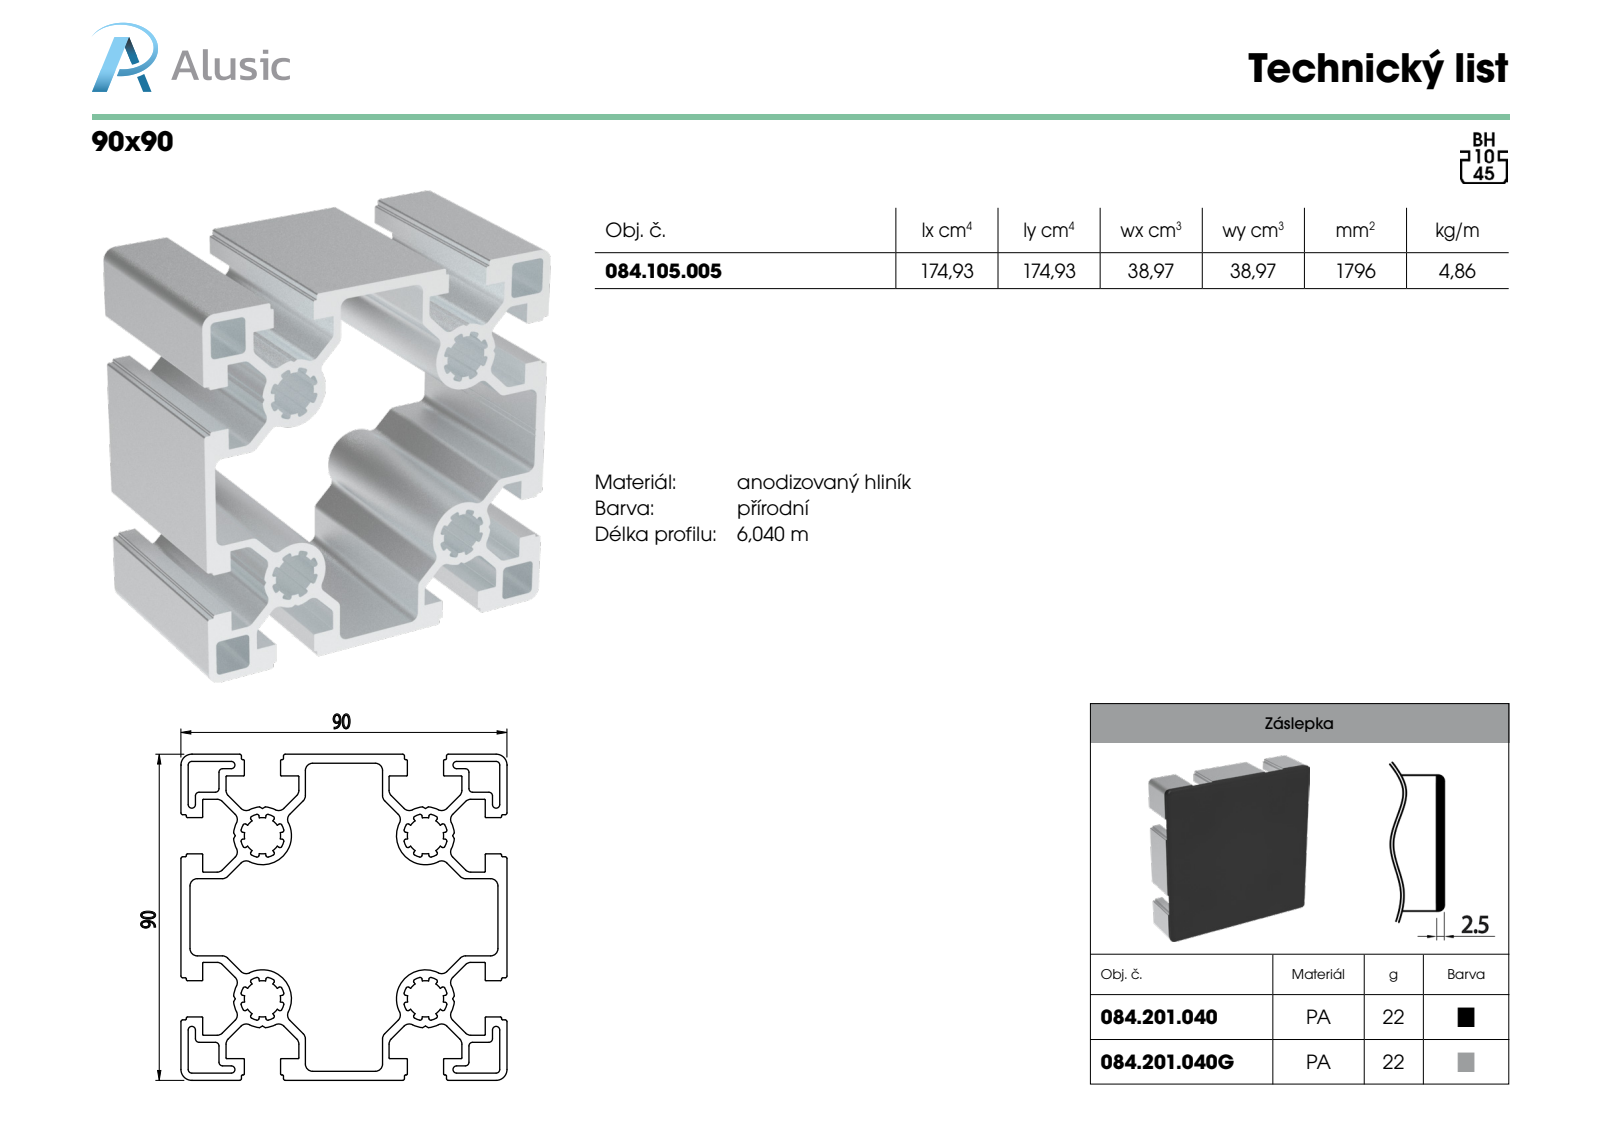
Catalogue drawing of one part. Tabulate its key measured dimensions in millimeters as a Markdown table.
| quantity | value |
| --- | --- |
| part name | 084.201.040 |
| STEP written by | SolidWorks 2011 (CONFIG_CONTROL_DESIGN) |
| units | millimeters |
| bodies | 1 solid, 58 faces (14 planar, 24 cylindrical, 20 other) |
| overall size | 90 × 90 × 10.5 |
| volume | 20 701 mm³ |
| surface area | 18 229 mm² |
| round holes (diameter × count) | 6.6 × 4 |
| round bosses / shafts (diameter × count) | 8.6 × 4 |
| partial cylindrical surfaces (radius × count) | 2 × 4, 2.5 × 4 |
| main face-to-face distances | 2.5, 90, 10.5, 8 |
| hole center spacings | 77.5, 109.6 |
